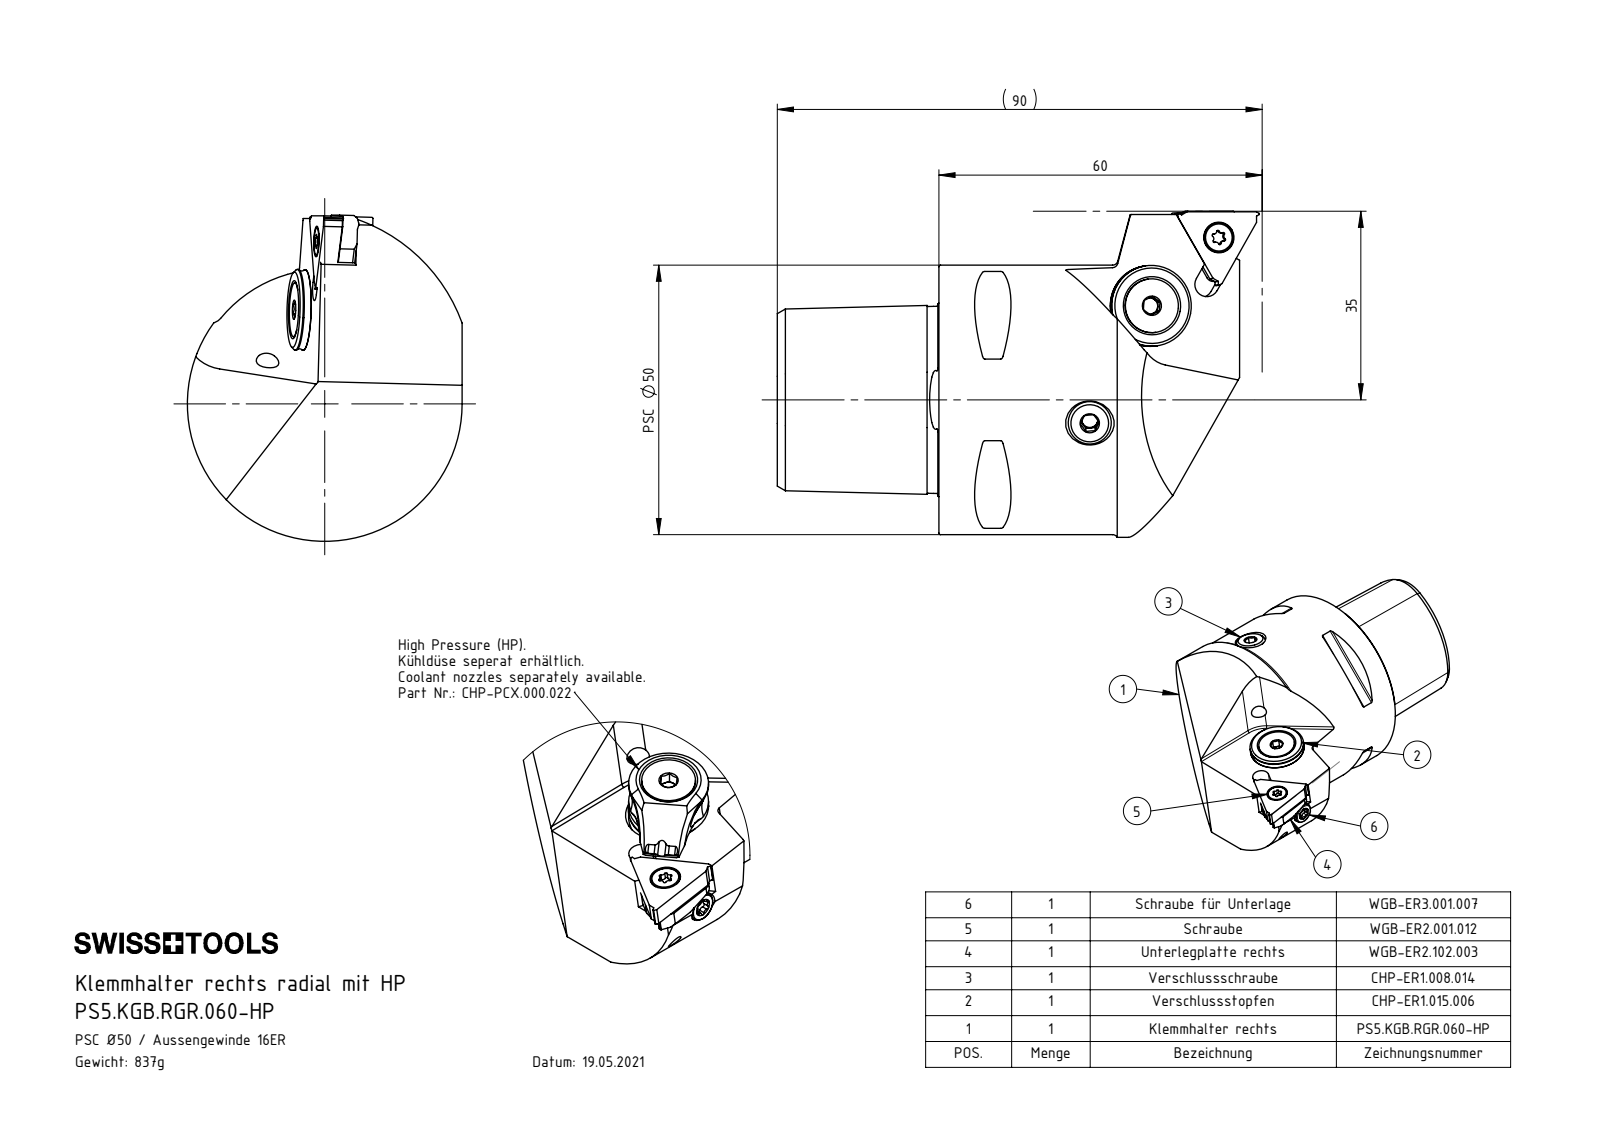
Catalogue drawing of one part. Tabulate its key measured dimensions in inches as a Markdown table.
| quantity | value |
| --- | --- |
| part name | WGB-ER3.001.007_A; CHP-ER1.015.006_A; WGB-ER2.001.012_A; WGB-ER2.102.003_A (+8 more) |
| STEP written by | SolidWorks 2017 (AUTOMOTIVE_DESIGN) |
| units | inches |
| bodies | 10 solids, 311 faces (127 planar, 85 cylindrical, 99 other) |
| overall size | 3.52 × 2.382 × 2.008 |
| volume | 6.564 in³ |
| surface area | 36.14 in² |
| round holes (diameter × count) | 0.165 × 3, 0.102 × 2, 0.157 × 2, 0.047 × 1, 0.079 × 1, 0.098 × 1, 0.118 × 1, 0.158 × 1, 0.197 × 1, 0.205 × 1, 0.24 × 1, 0.276 × 1 |
| round bosses / shafts (diameter × count) | 0.217 × 3, 1.969 × 1, 0.591 × 1, 0.528 × 1, 0.394 × 1, 0.315 × 1, 0.197 × 1, 0.125 × 1 |
| partial cylindrical surfaces (radius × count) | 0.02 × 10, 0.009 × 6, 0.013 × 6, 0.022 × 6, 0.022 × 6, 0.004 × 2, 0.01 × 1, 0.051 × 1 |
| main face-to-face distances | 1.181, 0.755, 0.057, 0.257, 0.069, 1.748, 0.189, 0.068, 0.189, 0.201 |
| hole center spacings | 0.178, 0.177, 0.178, 0.633, 0.634, 0.639, 0.64, 0.781 |
